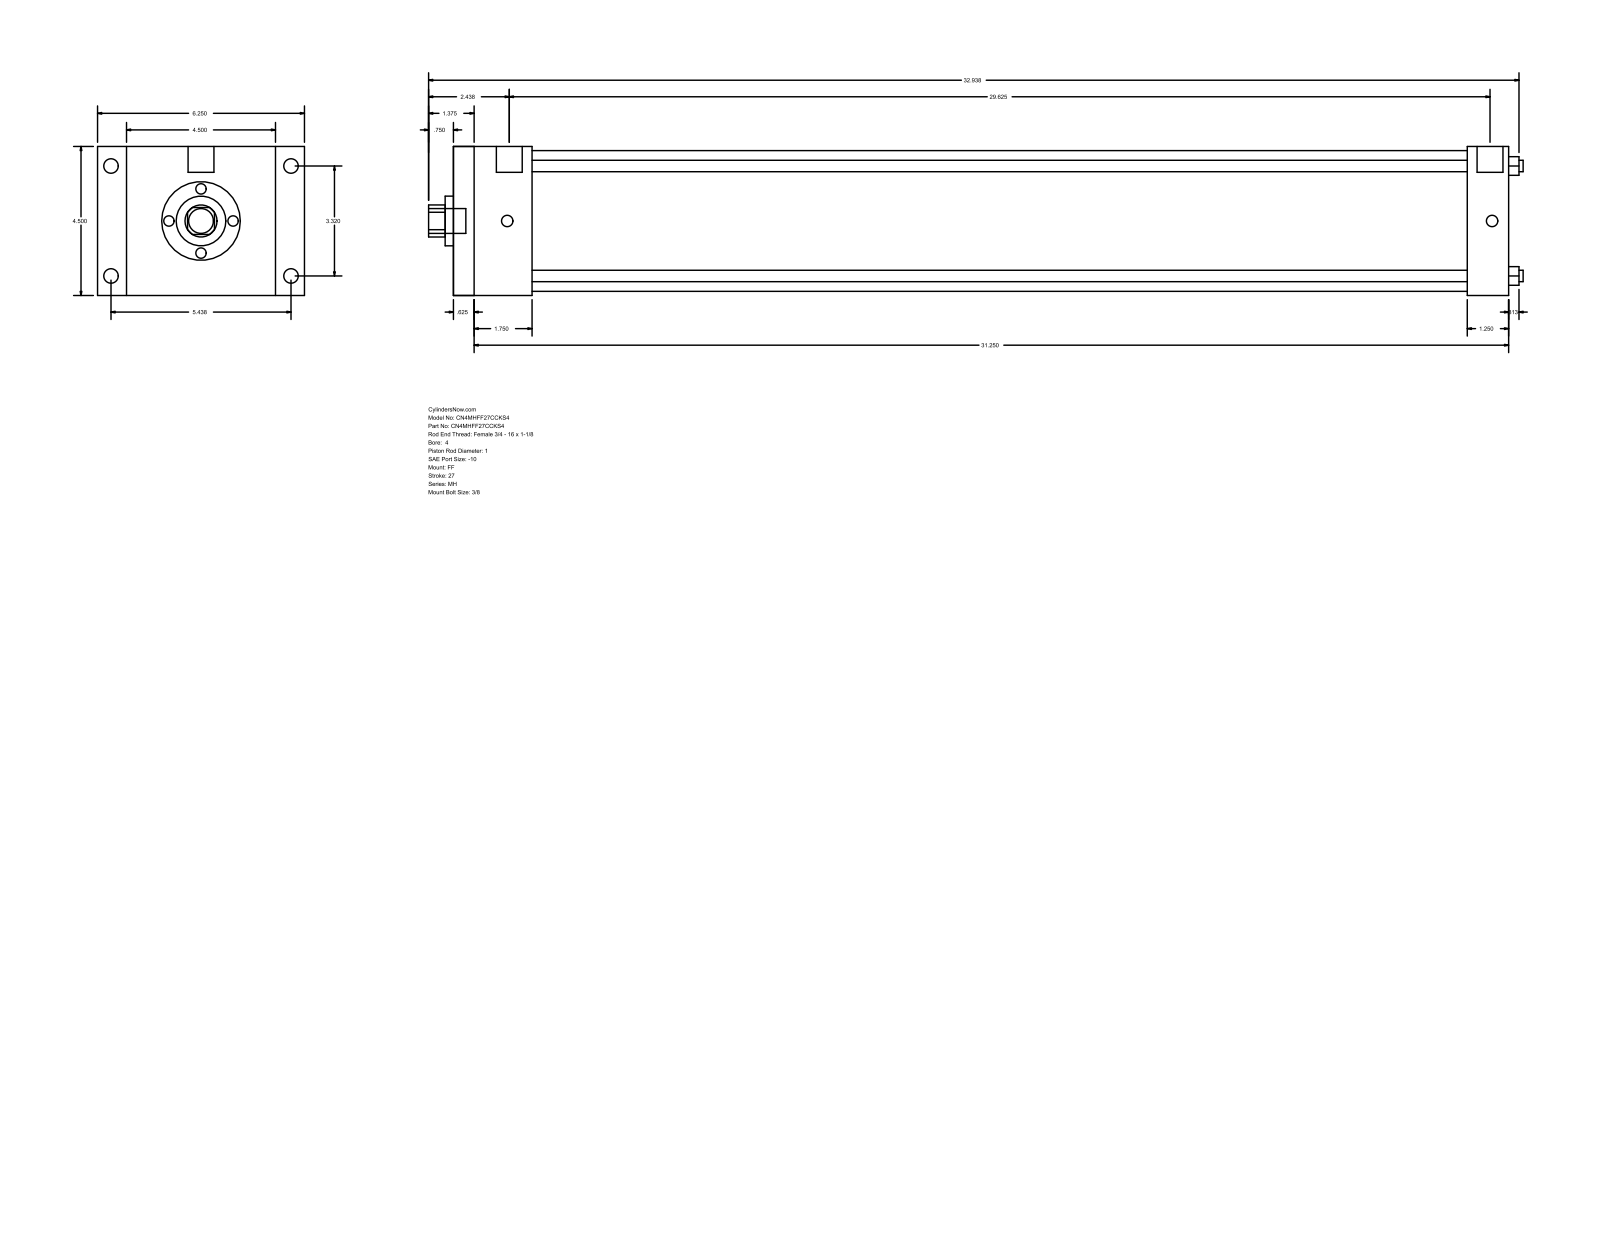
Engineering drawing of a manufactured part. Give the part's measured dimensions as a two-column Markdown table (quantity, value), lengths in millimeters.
| quantity | value |
| --- | --- |
| part name | MH_FF__0400_1 |
| STEP written by | GSSL Pune (CONFIG_CONTROL_DESIGN) |
| units | millimeters |
| bodies | 0 solids, 92 faces (64 planar, 28 cylindrical, 0 other) |
| overall size | 839.79 × 158.75 × 114.3 |
| round holes (diameter × count) | 8.76 × 4, 25.4 × 1, 38.1 × 1, 107.95 × 1 |
| round bosses / shafts (diameter × count) | 11.13 × 4, 8.73 × 4, 19.84 × 2, 19.05 × 1 |
| partial cylindrical surfaces (radius × count) | 12.29 × 1 |
| main face-to-face distances | 114.3, 809.62, 15.87, 793.75, 60.33, 44.46, 749.29, 777.87, 762, 717.54 |
| hole center spacings | 59.62, 84.32, 119.25 |
